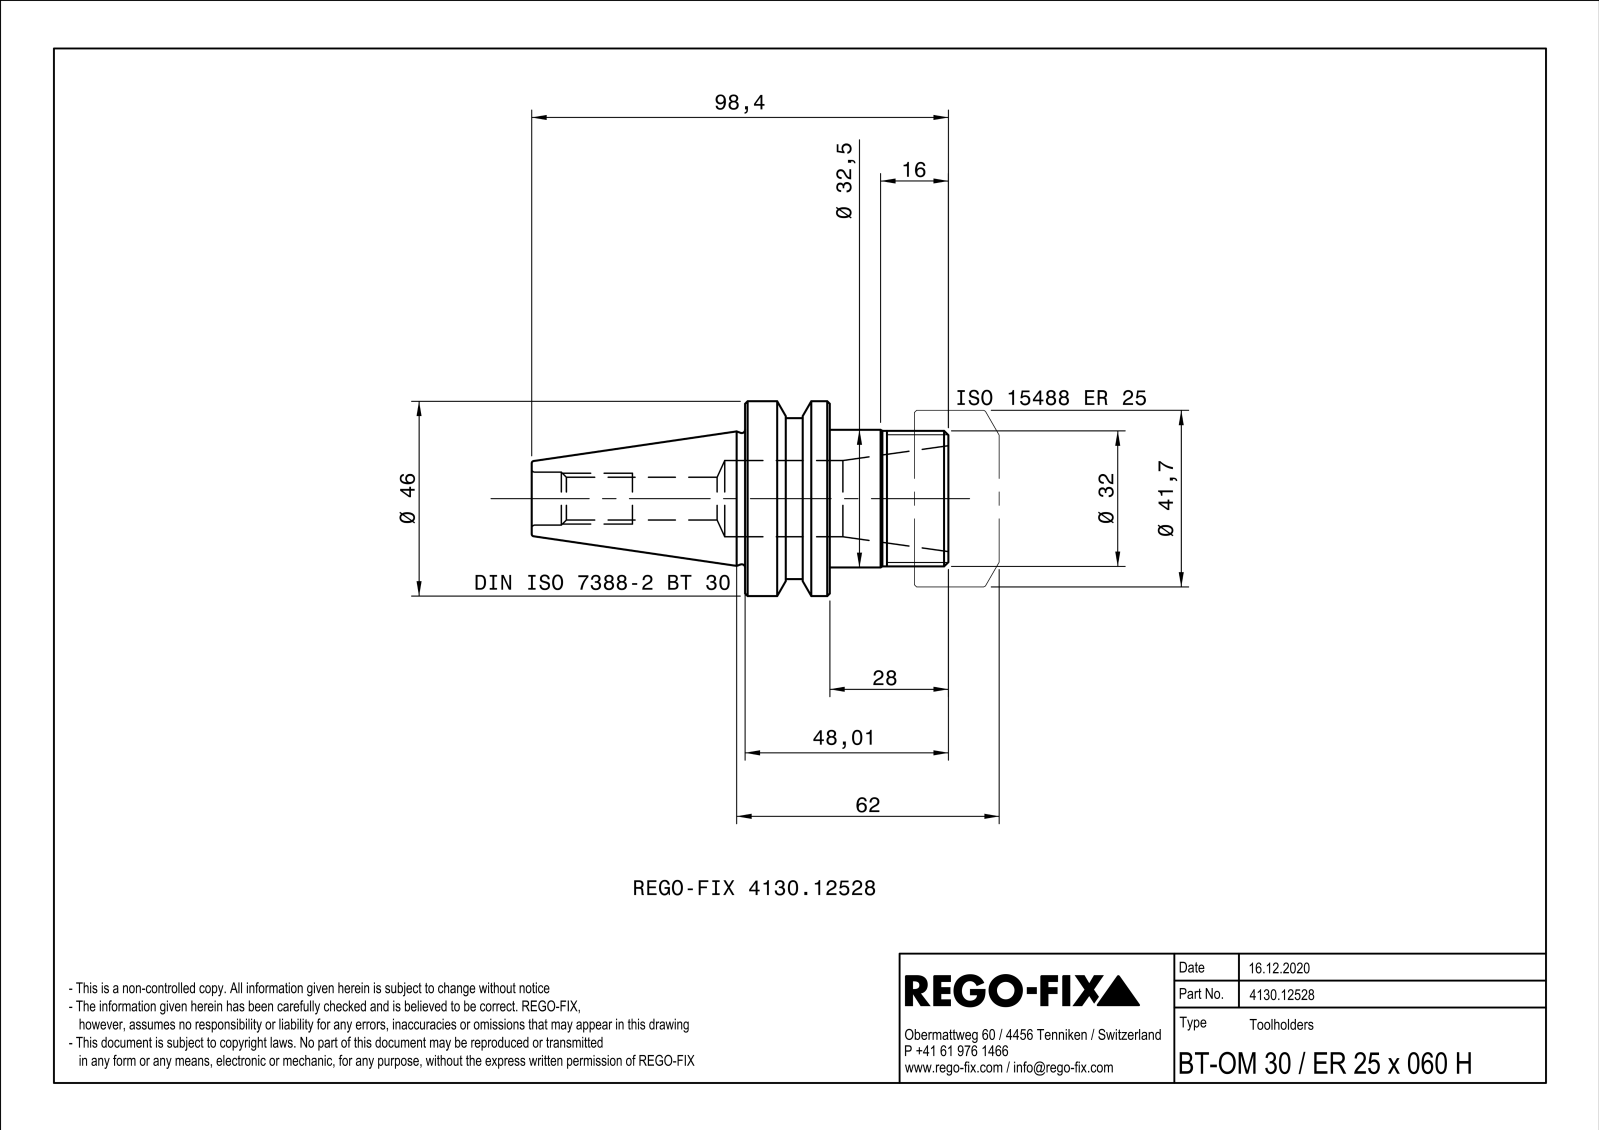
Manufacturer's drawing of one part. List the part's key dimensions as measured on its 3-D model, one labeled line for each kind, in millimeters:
Part name (STEP PRODUCT): NOCUT
STEP written by: SIEMENS PLM Software Solid Edge ST10 (AUTOMOTIVE_DESIGN)
Units: millimetres
Bodies: 1 solid, 48 faces (7 planar, 14 cylindrical, 27 other)
Overall size (bounding box): 98.4 × 46 × 46
Volume: 57 666 mm³ · Surface area: 17 139 mm²
Round holes (diameter × count): ⌀10.11 ×1, ⌀12.5 ×1, ⌀18 ×1
Round bosses / shafts (diameter × count): ⌀46 ×1, ⌀38 ×1, ⌀32.5 ×1, ⌀32 ×1
Main face-to-face distances: 20, 28, 48, 98.4, 70.4, 50.4, 38.4, 10.4, 9.6, 60
